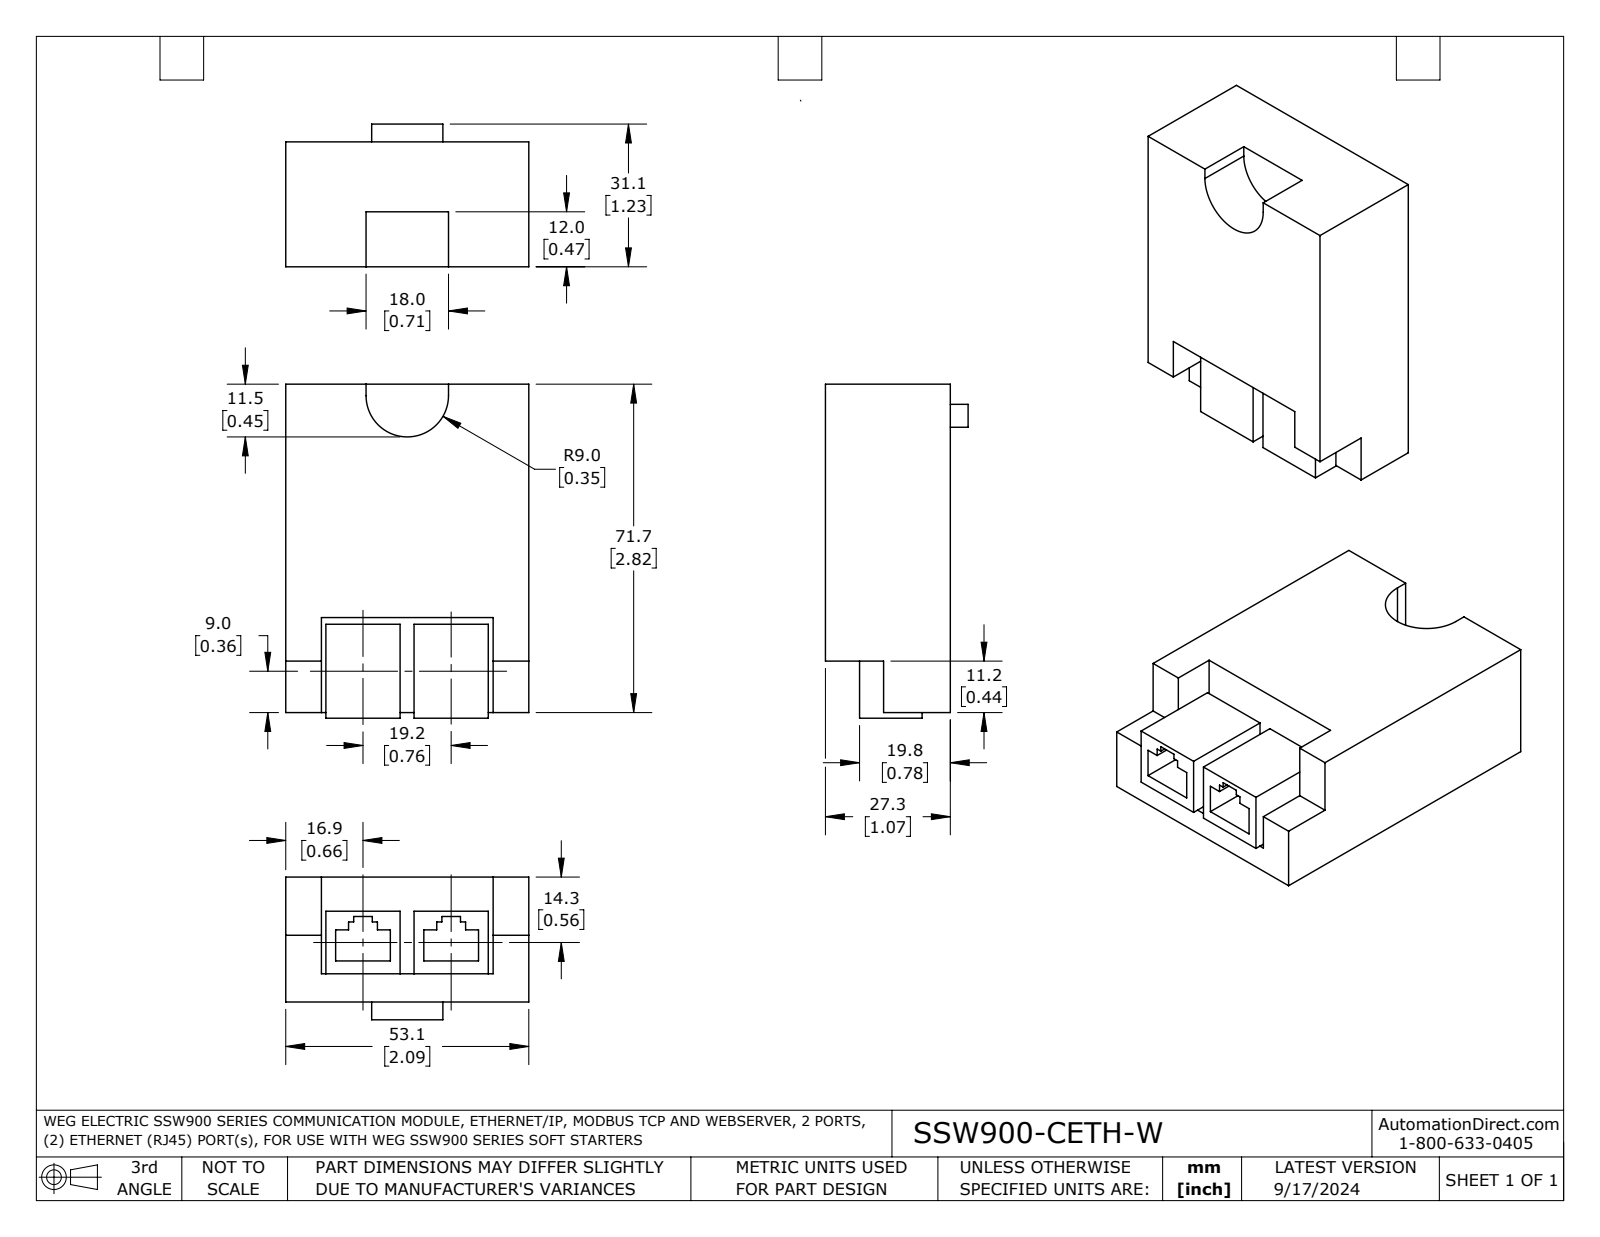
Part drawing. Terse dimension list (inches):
name: SSW900-CETH-W
written by: SolidWorks 2021 (AUTOMOTIVE_DESIGN)
unit: in
bodies: 1 solid, 61 faces (60 planar, 1 cylindrical, 0 other)
size: 2.869 × 2.089 × 1.226
volume: 5.42 in³; area: 28.97 in²
rounds: 1× R0.354
face distances: 1.073, 2.089, 2.005, 0.78, 0.293, 0.306, 1.782, 0.638, 0.757, 0.816
